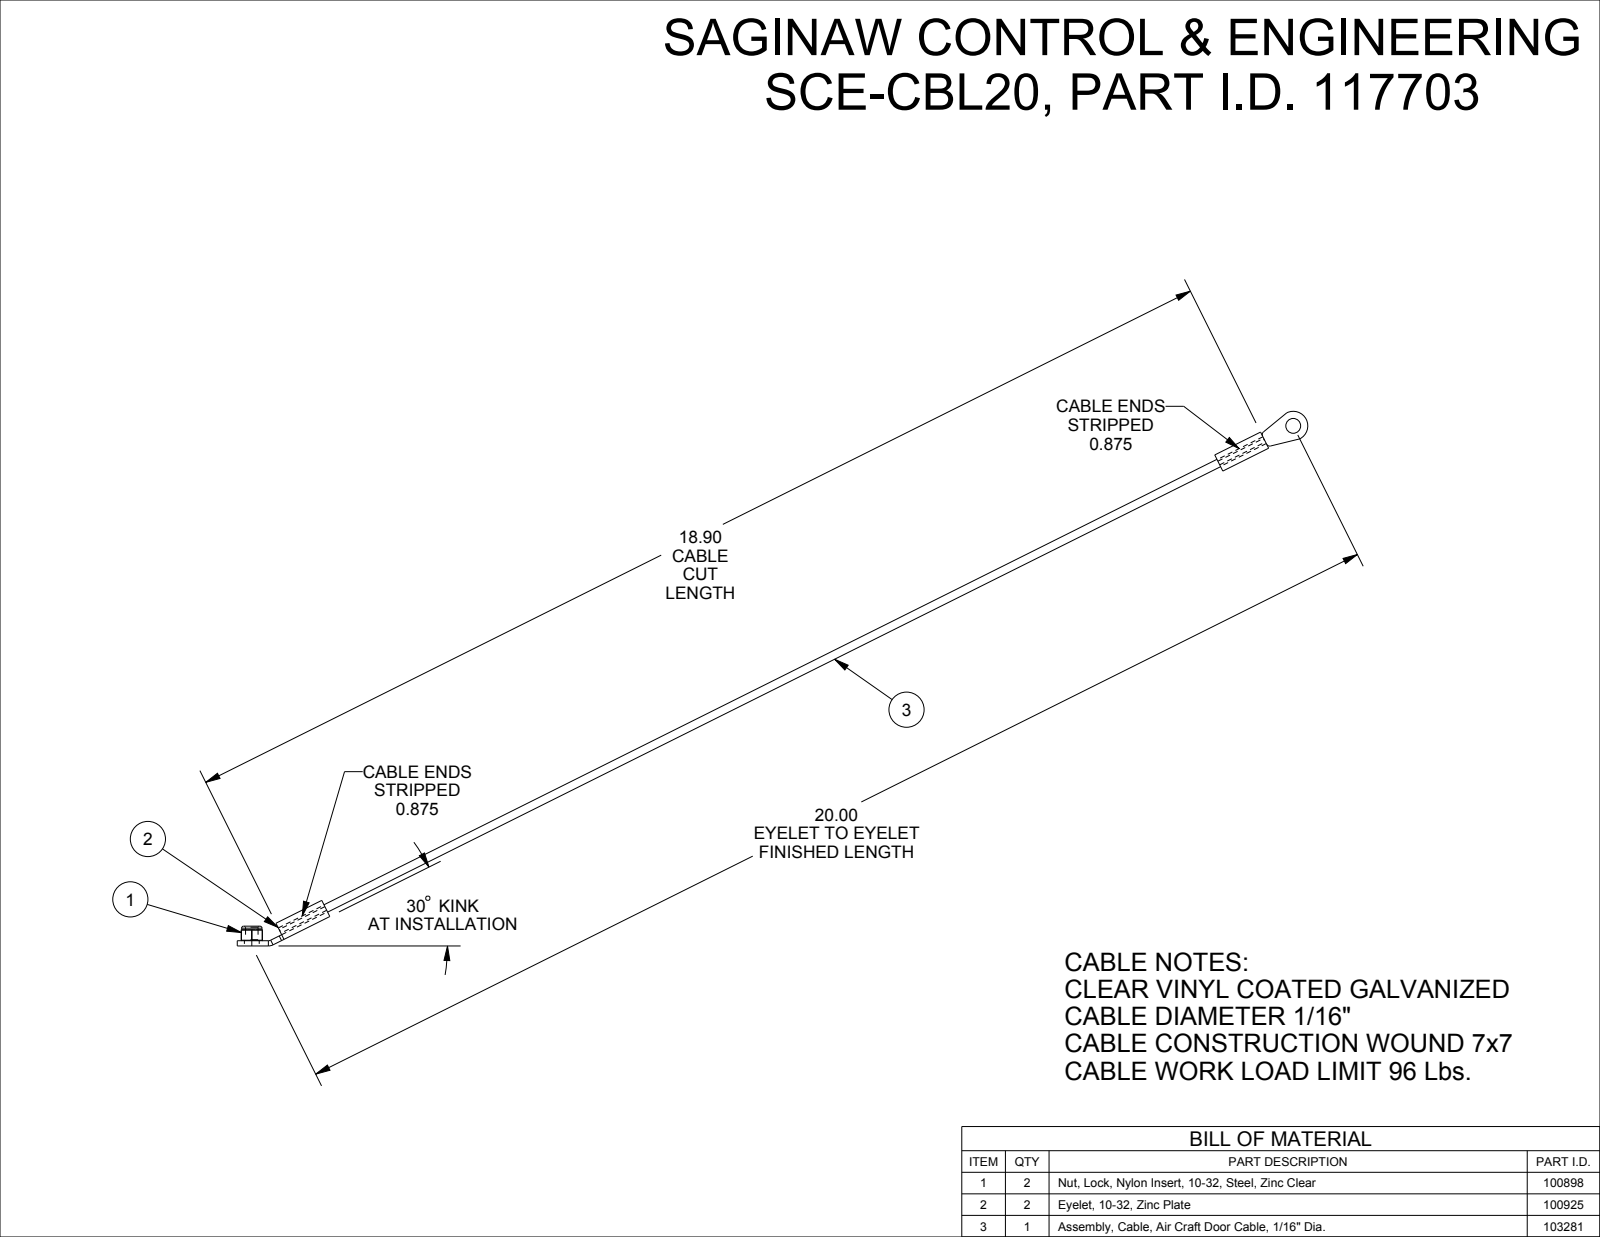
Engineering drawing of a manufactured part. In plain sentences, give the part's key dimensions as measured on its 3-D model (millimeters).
The part is named "SCE-CBL20". Its 3-D file was written by "SolidWorks 2019 (AUTOMOTIVE_DESIGN)". It is 6 solids with 78 faces: 36 planar, 37 cylindrical and 5 other. Overall it measures 520.2 by 15.5 by 12.7 millimeters. Its volume is 7 340 cubic millimeters and its surface area 8 277 square millimeters. Round holes: 1 of diameter 3.3, 1 of diameter 5.5, 1 of diameter 6.5, 1 of diameter 6.5. Round bosses or shafts: 1 of diameter 8.9, 1 of diameter 7.9, 1 of diameter 3.6, 1 of diameter 1.8. Partial cylindrical surfaces (rounded edges, fillets, slot ends): 18 of radius 0.2, 4 of radius 1.5, 2 of radius 6.4, 1 of radius 2.3, 1 of radius 4.6. The main face-to-face distances are 2.3, 2.3, 22.4, 458, 480.3, 435.6, 9.3, 9.3, 6.4, 8.6.
